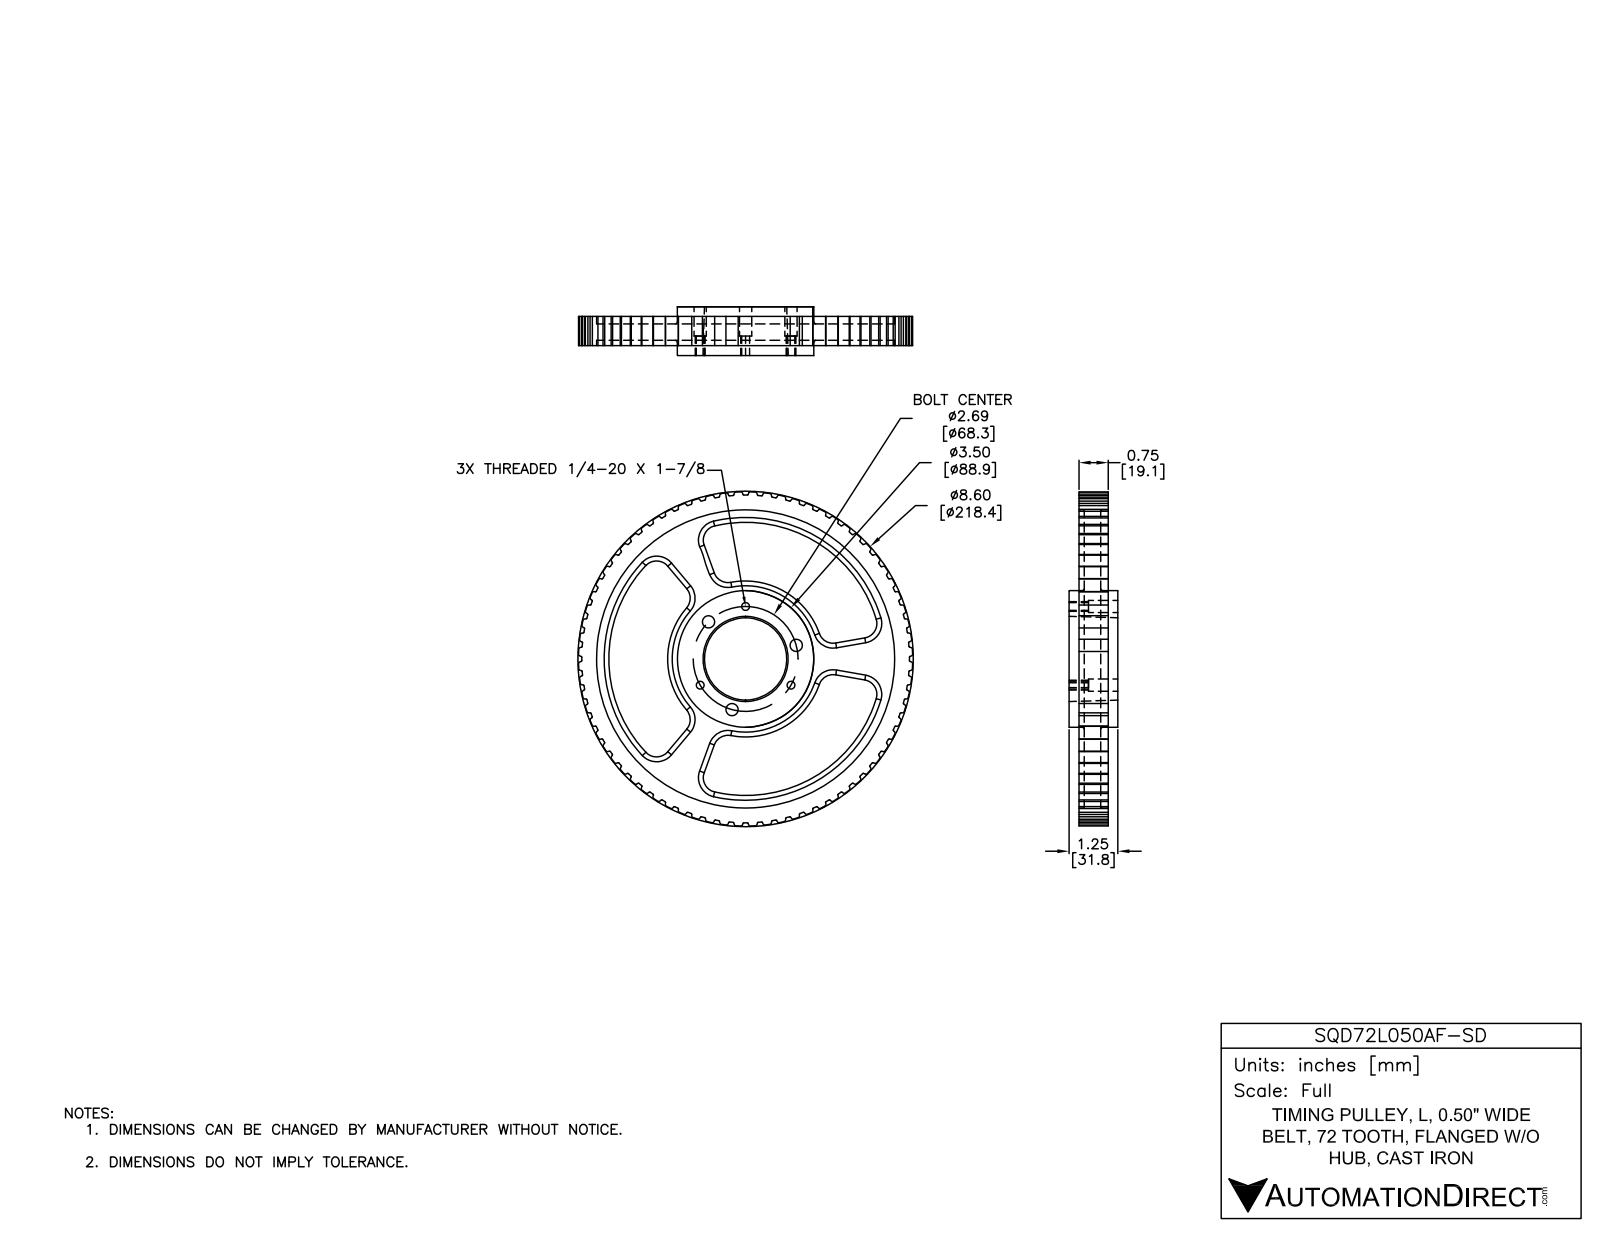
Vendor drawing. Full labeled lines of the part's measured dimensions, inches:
Part name (STEP PRODUCT): SQD72L050AF-SD
STEP written by: SolidWorks 2014 (AUTOMOTIVE_DESIGN)
Units: inches
Bodies: 1 solid, 759 faces (231 planar, 474 cylindrical, 54 other)
Overall size (bounding box): 8.564 × 8.564 × 1.25
Volume: 20.3 in³ · Surface area: 129.8 in²
Round holes (diameter × count): ⌀0.201 ×3, ⌀0.31 ×3, ⌀0.313 ×3, ⌀7.625 ×1
Round bosses / shafts (diameter × count): ⌀3.375 ×1
Partial cylindrical surfaces — rounded edges, fillets, slot ends (radius × count): R0.021 ×144, R0.03 ×144, R0.125 ×12, R0.375 ×12, R2 ×1, R3.5 ×1, R4.284 ×1
Main face-to-face distances: 0.18, 0.57, 0.75, 0.25, 0.43, 0.82, 1, 0.39, 1.25, 2.819
Hole centre spacings: 1.344, 2.327, 2.328, 2.665, 1.028, 1.636, 1.029, 1.343
